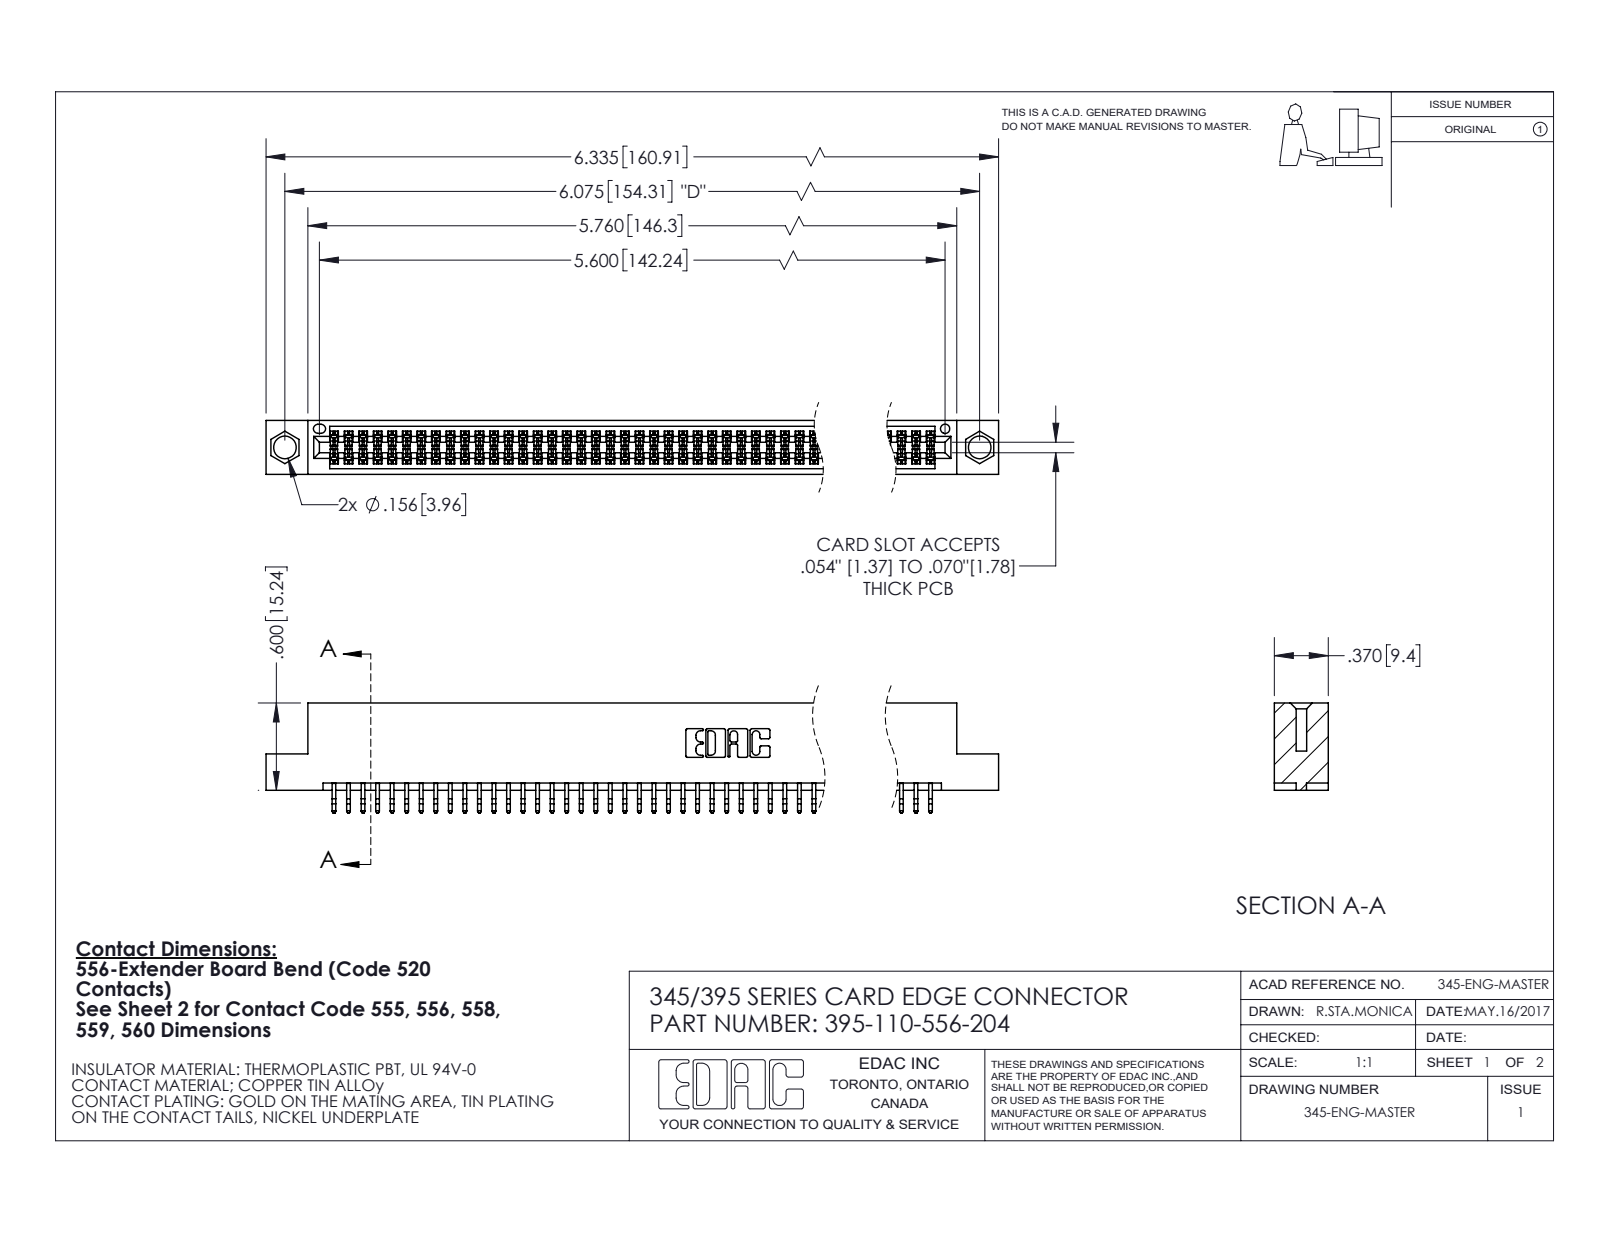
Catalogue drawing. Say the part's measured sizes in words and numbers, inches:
The part is named "345 Part_Flush Mounting Lugs - 0.156 Dia-TI; 395-110-556-204; 345-292-001_556 Tail". Its 3-D file was written by "SolidWorks 2020 (CONFIG_CONTROL_DESIGN)". It is 111 solids with 6300 faces: 4164 planar, 2136 cylindrical and 0 other. Overall it measures 6.335 by 0.757 by 0.37 inches. Its volume is 0.954 cubic inches and its surface area 35.85 square inches. Round holes: 2 of diameter 0.156, 1 of diameter 0.064. Partial cylindrical surfaces (rounded edges, fillets, slot ends): 220 of radius 0.006, 22 of radius 0.01, 6 of radius 0.007, 6 of radius 0.031, 3 of radius 0.026, 2 of radius 0.01, 2 of radius 0.014, 2 of radius 0.019. The main face-to-face distances are 0.298, 0.072, 0.37, 0.2, 0.025, 0.098, 0.272, 0.225, 0.175, 0.149. The hole center spacings are 0.27, 5.839, 6.075.
